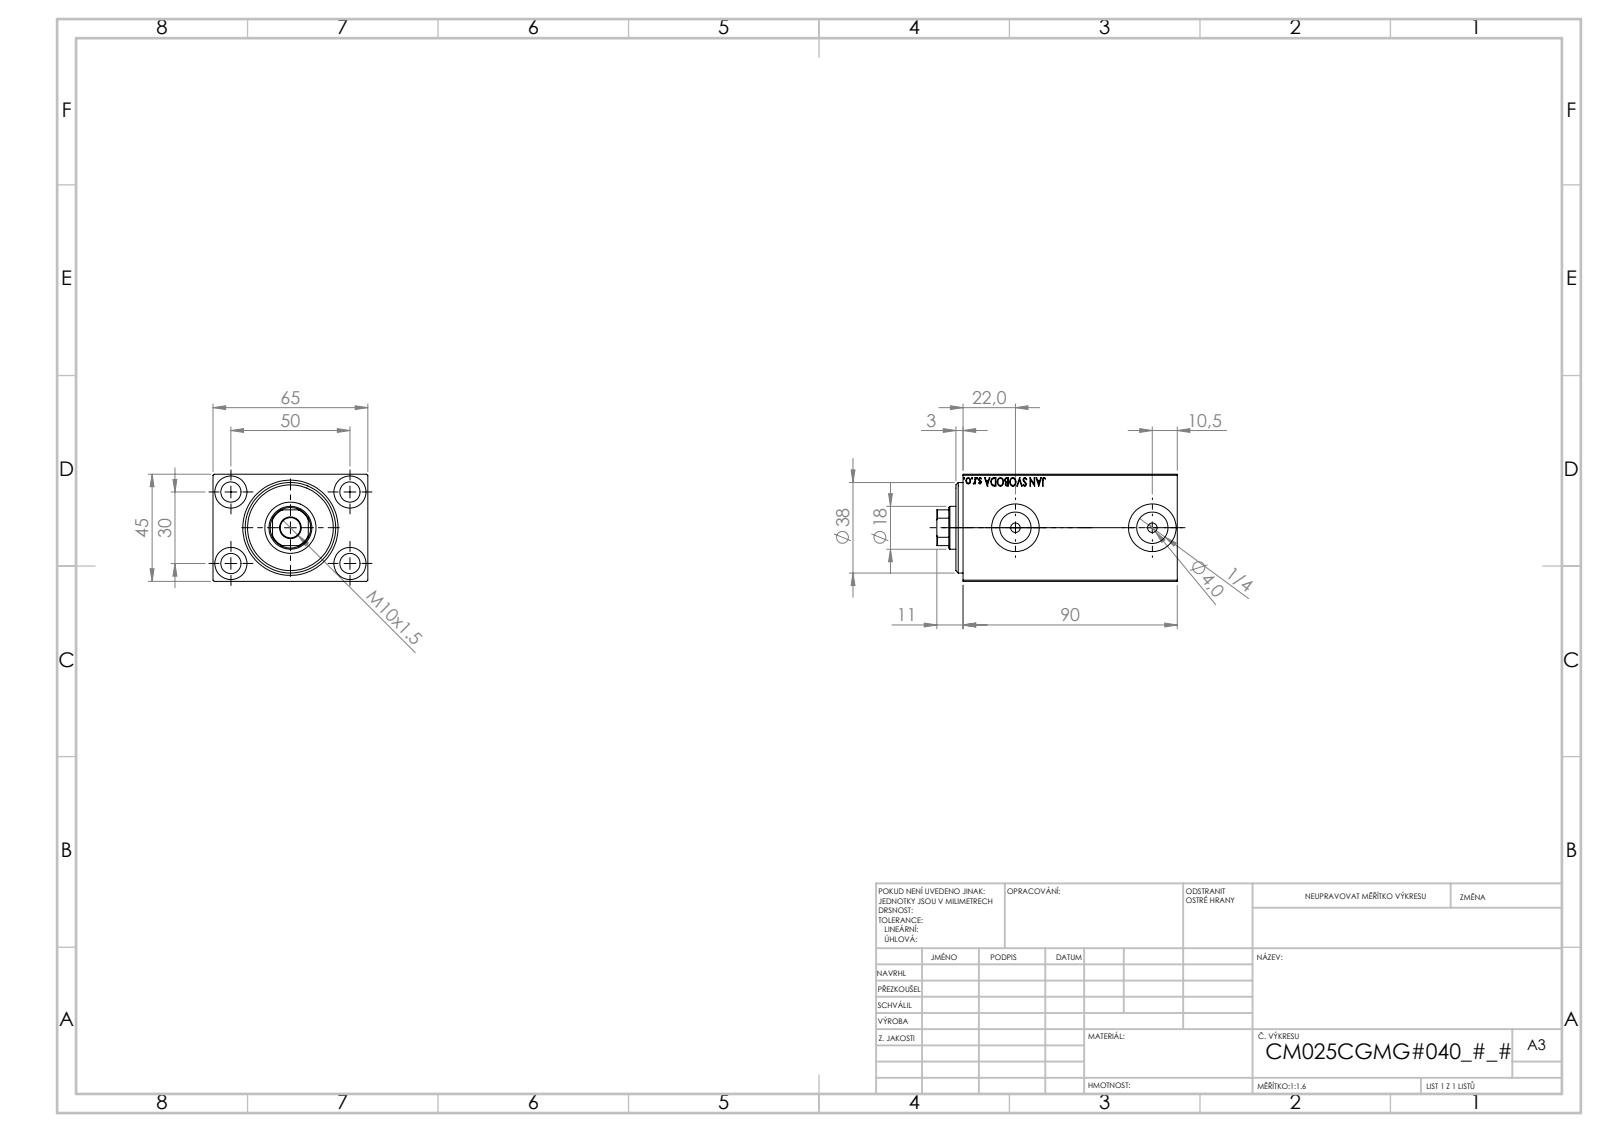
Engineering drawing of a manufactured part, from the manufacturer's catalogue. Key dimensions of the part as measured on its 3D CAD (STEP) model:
Part name (STEP PRODUCT): V450CM_C_VCP; V450CM_VC_B; V450CM_C_Body
STEP written by: SolidWorks 2019 (CONFIG_CONTROL_DESIGN)
Units: millimetres
Bodies: 3 solids, 862 faces (408 planar, 60 cylindrical, 394 other)
Overall size (bounding box): 101 × 65 × 45
Volume: 227 267 mm³ · Surface area: 55 379 mm²
Round holes (diameter × count): ⌀8.5 ×5, ⌀13.5 ×4, ⌀4 ×2, ⌀13.16 ×2, ⌀20 ×2, ⌀18 ×1, ⌀21.5 ×1, ⌀25 ×1, ⌀27 ×1, ⌀38 ×1
Partial cylindrical surfaces — rounded edges, fillets, slot ends (radius × count): R8.5 ×1
Main face-to-face distances: 45, 65, 6, 79, 84, 85, 5, 90, 3, 8
Hole centre spacings: 29.15, 30, 50, 58.31, 57.5
